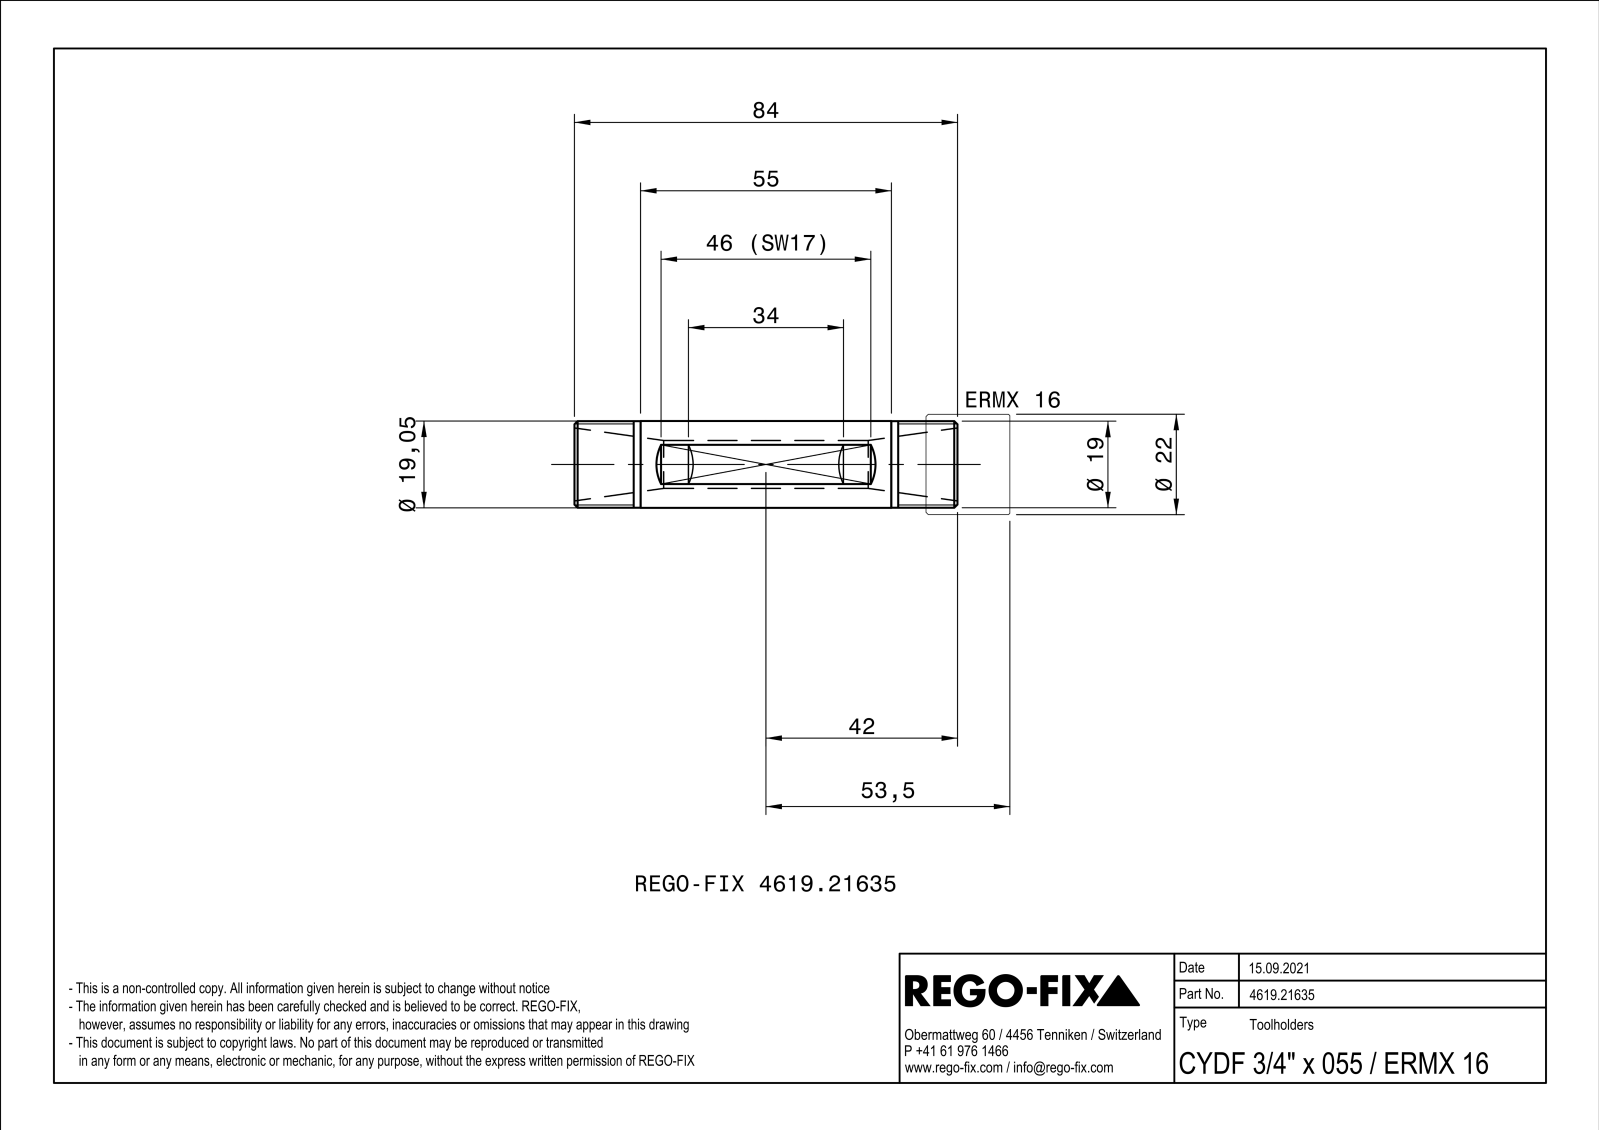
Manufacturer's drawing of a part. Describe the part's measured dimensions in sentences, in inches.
The part is named "NOCUT". Its 3-D file was written by "SIEMENS PLM Software Solid Edge ST10 (AUTOMOTIVE_DESIGN)". It is 1 solid with 25 faces: 11 planar, 6 cylindrical and 8 other. Overall it measures 3.307 by 0.75 by 0.75 inches. Its volume is 0.864 cubic inches and its surface area 12.79 square inches. Round holes: 1 of diameter 0.413. Round bosses or shafts: 1 of diameter 0.75, 1 of diameter 0.748. The main face-to-face distances are 0.669, 3.307, 0.306, 1.113, 0.807.
